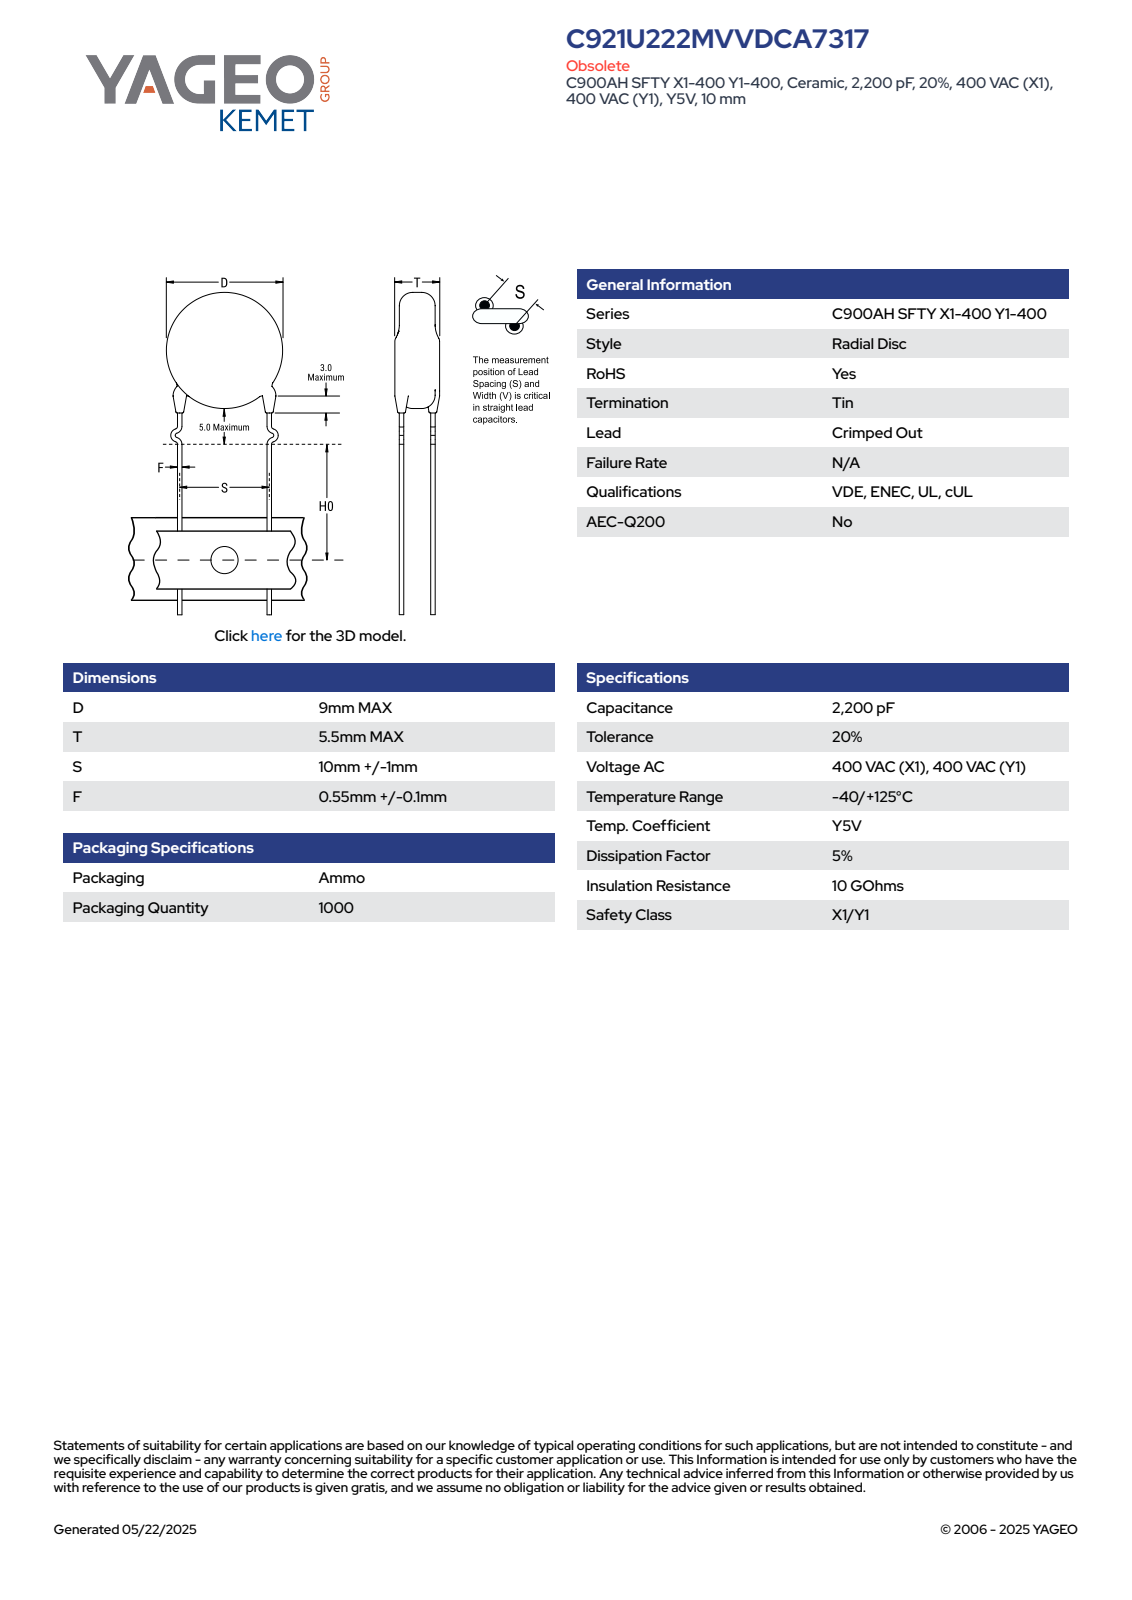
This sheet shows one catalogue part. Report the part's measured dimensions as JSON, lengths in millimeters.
{"part_name": "CCD_KCOC900_D9T5.5S10LL20F0.55", "step_written_by": "SolidWorks 2014 (AUTOMOTIVE_DESIGN)", "units": "millimeters", "bodies": {"solids": 4, "faces": 93, "planar": 63, "cylindrical": 10, "other": 20}, "overall_size": [34, 14.29, 6.24], "volume_mm3": 364, "surface_area_mm2": 399, "round_bosses_or_shafts": [[1.2, 2], [9, 1]], "partial_cylinders_radius": [[0.6, 2]], "face_to_face_distances": [5.5, 0.94, 4.98, 4.04, 0.76, 3.82, 0.58, 4.07, 2.77, 2.88]}
